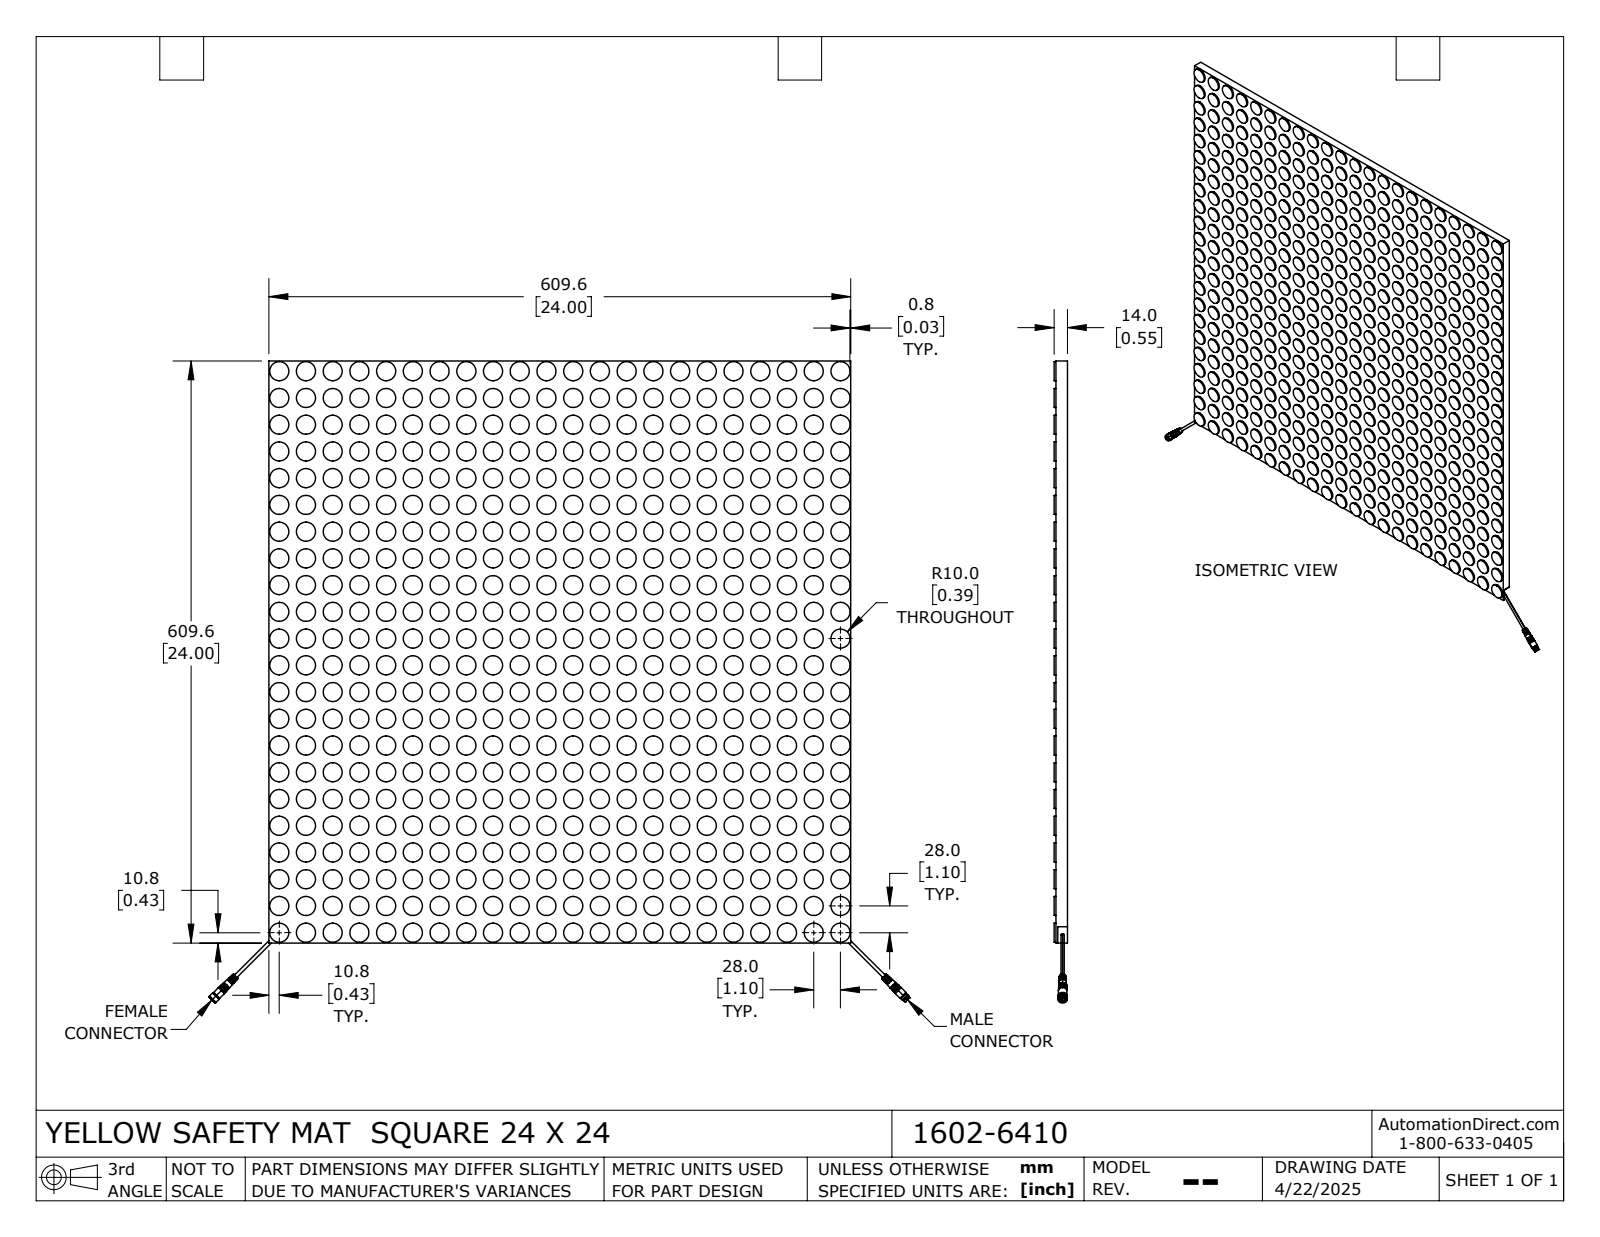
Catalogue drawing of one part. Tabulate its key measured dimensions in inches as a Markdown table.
| quantity | value |
| --- | --- |
| part name | 1602-6410 |
| STEP written by | SolidWorks 2024 (AUTOMOTIVE_DESIGN) |
| units | inches |
| bodies | 20 solids, 1836 faces (612 planar, 1086 cylindrical, 138 other) |
| overall size | 28.904 × 26.474 × 0.551 |
| volume | 290.8 in³ |
| surface area | 1 300 in² |
| round holes (diameter × count) | 0.063 × 3, 0.134 × 2, 0.228 × 1, 0.232 × 1, 0.272 × 1, 0.283 × 1 |
| round bosses / shafts (diameter × count) | 0.787 × 484, 0.047 × 24, 0.031 × 8, 0.039 × 3, 0.346 × 2, 0.138 × 2, 0.378 × 1, 0.354 × 1 |
| main face-to-face distances | 0.472, 0.079, 0.551, 24, 0.087, 0.394, 0.157, 0.173, 0.039, 0.047 |
| hole center spacings | 0.069, 0.098, 0.138 |
